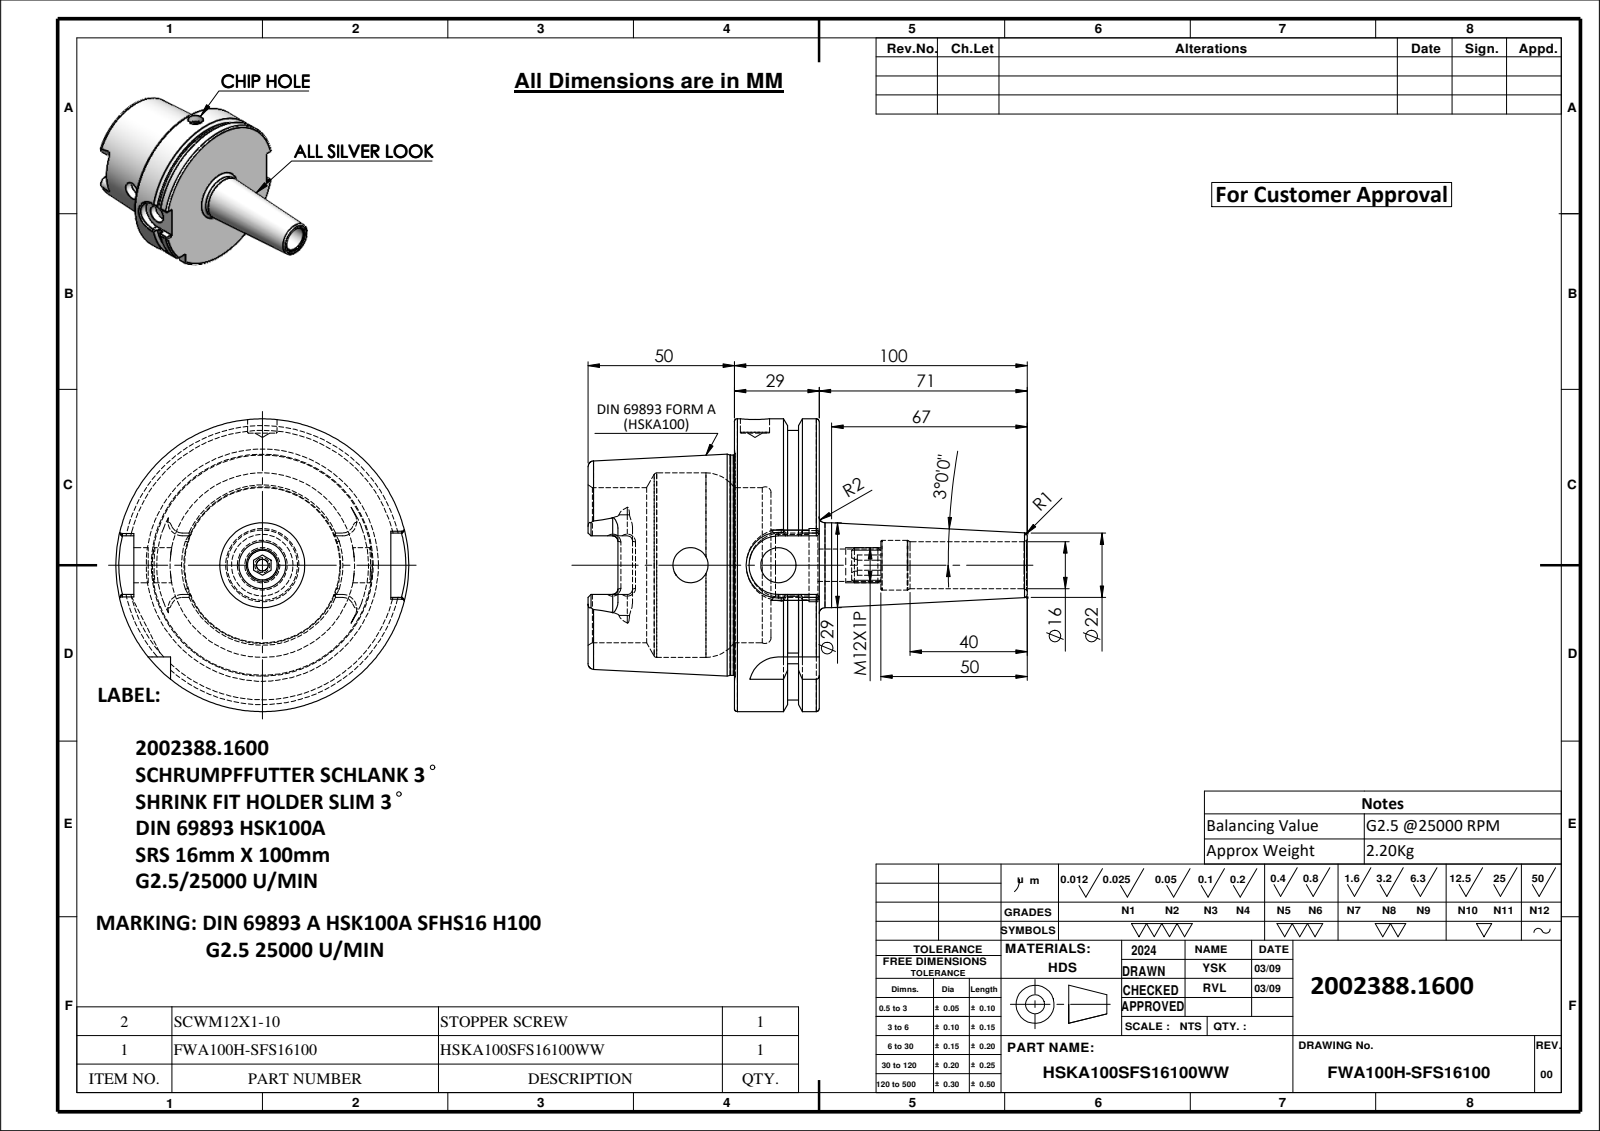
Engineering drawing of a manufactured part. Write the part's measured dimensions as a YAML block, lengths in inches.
part_name: "HSKA100SFS16100WW; FWA100H-SFS16100; SCWM12X1-10"
step_written_by: "SolidWorks 2024 (CONFIG_CONTROL_DESIGN)"
units: inches
bodies: {solids: 2, faces: 201, planar: 61, cylindrical: 56, other: 84}
overall_size: [5.906, 3.937, 3.937]
volume: 17.05
surface_area: 91.56
round_holes:
  - {diameter: 0.472, count: 2}
  - {diameter: 0.157, count: 1}
  - {diameter: 0.394, count: 1}
  - {diameter: 0.433, count: 1}
  - {diameter: 0.63, count: 1}
  - {diameter: 0.669, count: 1}
  - {diameter: 0.827, count: 1}
  - {diameter: 0.984, count: 1}
  - {diameter: 2.087, count: 1}
  - {diameter: 2.48, count: 1}
round_bosses_or_shafts:
  - {diameter: 3.937, count: 1}
  - {diameter: 3.622, count: 1}
  - {diameter: 2.959, count: 1}
  - {diameter: 1.142, count: 1}
  - {diameter: 0.472, count: 1}
partial_cylinders:
  - {radius: 0.071, count: 6}
  - {radius: 0.192, count: 4}
  - {radius: 0.394, count: 2}
  - {radius: 0.433, count: 1}
face_to_face_distances: [1.14, 0.492, 0.648, 1.969, 2.461, 3.108, 2.83, 0.861, 0.369, 0.279]
hole_center_spacings: [1.181]
